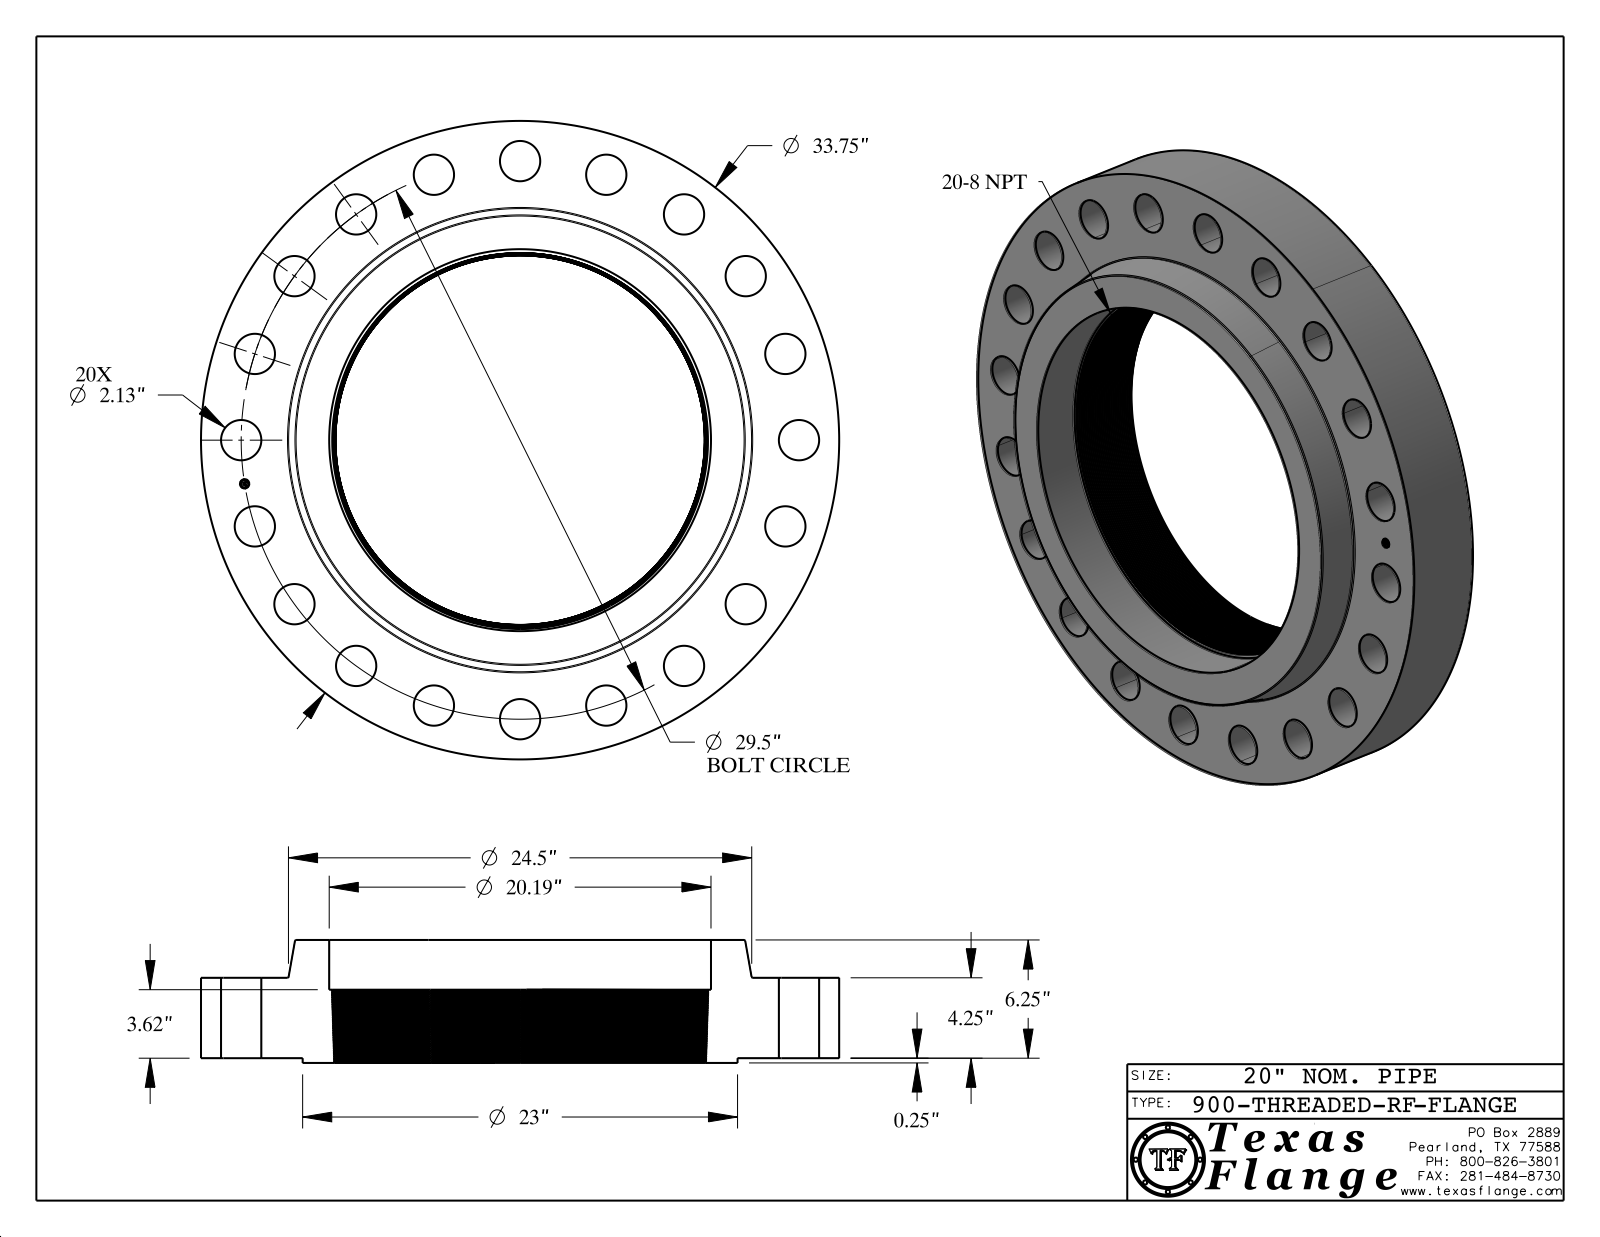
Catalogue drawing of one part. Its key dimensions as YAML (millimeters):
part_name: "900-THREADED-RF"
step_written_by: "CATIA V5 STEP AP214 (AUTOMOTIVE_DESIGN)"
units: millimeters
bodies: {solids: 1, faces: 758, planar: 370, cylindrical: 66, other: 322}
overall_size: [857.3, 857.3, 165.1]
volume: 40840000
surface_area: 1815000
round_holes:
  - {diameter: 54.1, count: 20}
  - {diameter: 12.6, count: 1}
  - {diameter: 512.8, count: 1}
round_bosses_or_shafts:
  - {diameter: 0.8, count: 8}
  - {diameter: 857.3, count: 1}
  - {diameter: 584.2, count: 1}
  - {diameter: 9.9, count: 1}
face_to_face_distances: [108, 158.8, 50.8, 6.4, 114.3, 165.1, 98.3, 91.9, 16, 66.8]
hole_center_spacings: [374.7, 740.1, 117.2, 440.4, 529.8, 606.2, 667.6, 231.5]
